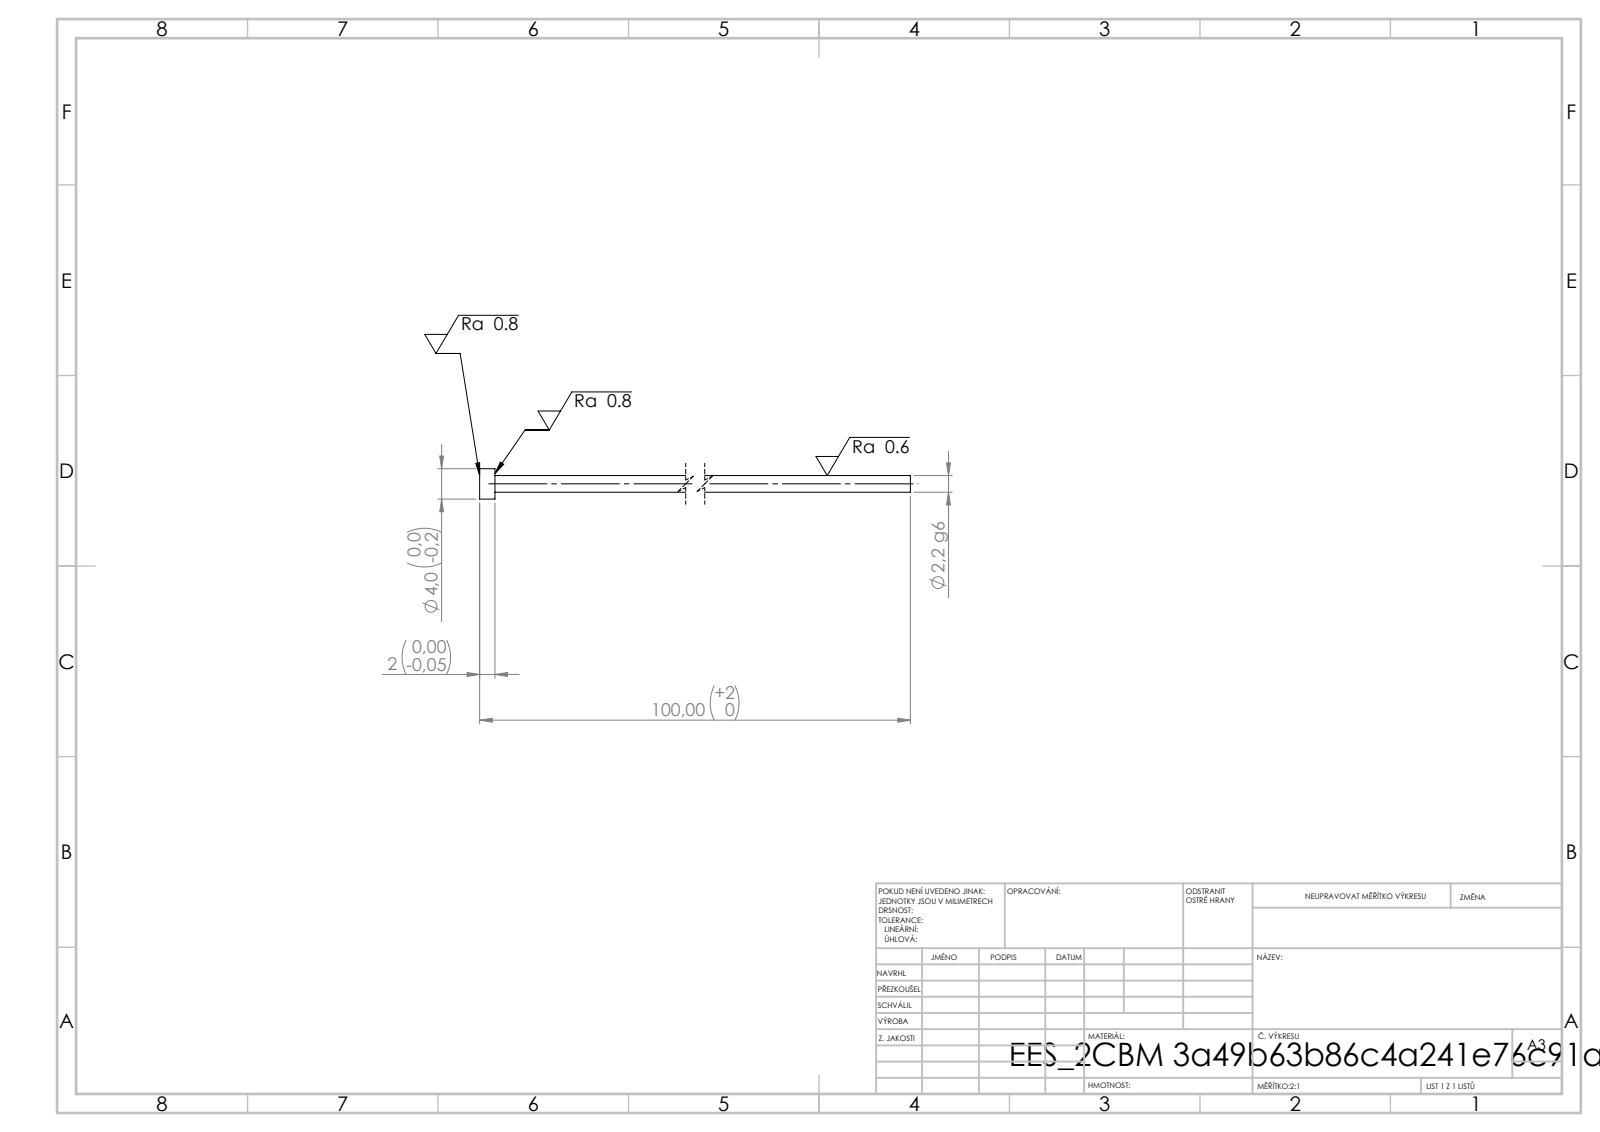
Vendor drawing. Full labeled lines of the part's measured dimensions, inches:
STEP written by: SolidWorks 2019 (CONFIG_CONTROL_DESIGN)
Units: inches
Bodies: 1 solid, 7 faces (3 planar, 4 cylindrical, 0 other)
Overall size (bounding box): 3.937 × 0.157 × 0.157
Volume: 0.024 in³ · Surface area: 1.13 in²
Round bosses / shafts (diameter × count): ⌀0.157 ×1, ⌀0.087 ×1
Main face-to-face distances: 0.079, 3.937, 3.858
